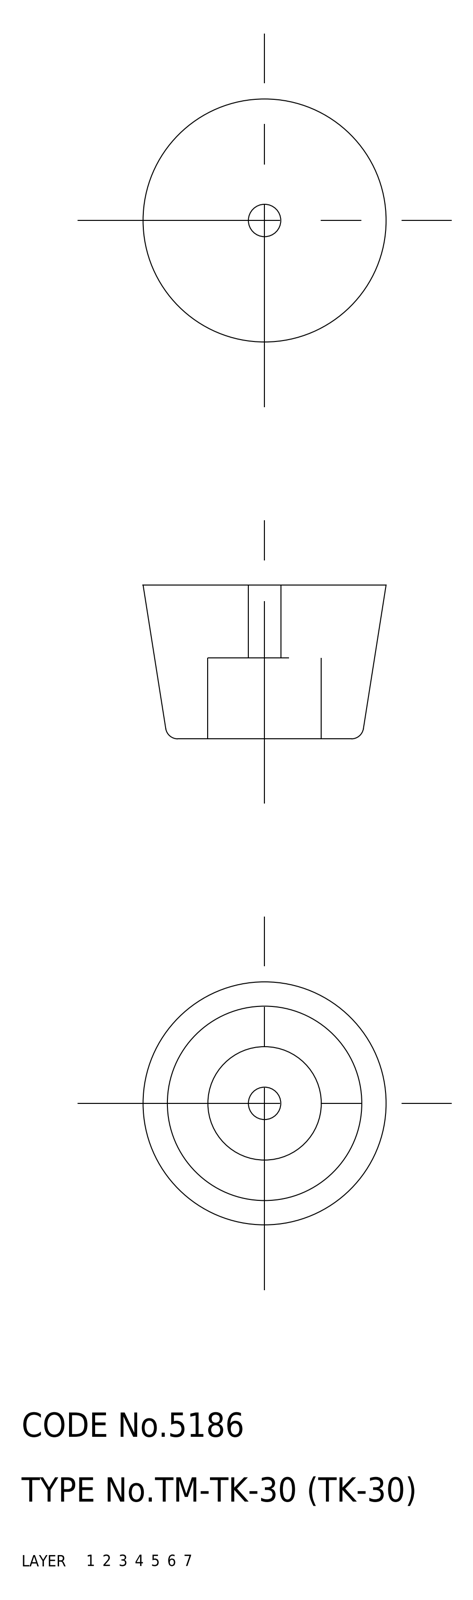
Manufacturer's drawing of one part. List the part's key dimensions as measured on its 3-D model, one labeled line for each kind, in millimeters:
Part name (STEP PRODUCT): washer; rubber foot; TK_30_9630_36
STEP written by: CADfix (AUTOMOTIVE_DESIGN)
Units: millimetres
Bodies: 2 solids, 20 faces (0 planar, 0 cylindrical, 20 other)
Overall size (bounding box): 30 × 30 × 19
Volume: 9 268 mm³ · Surface area: 3 838 mm²
